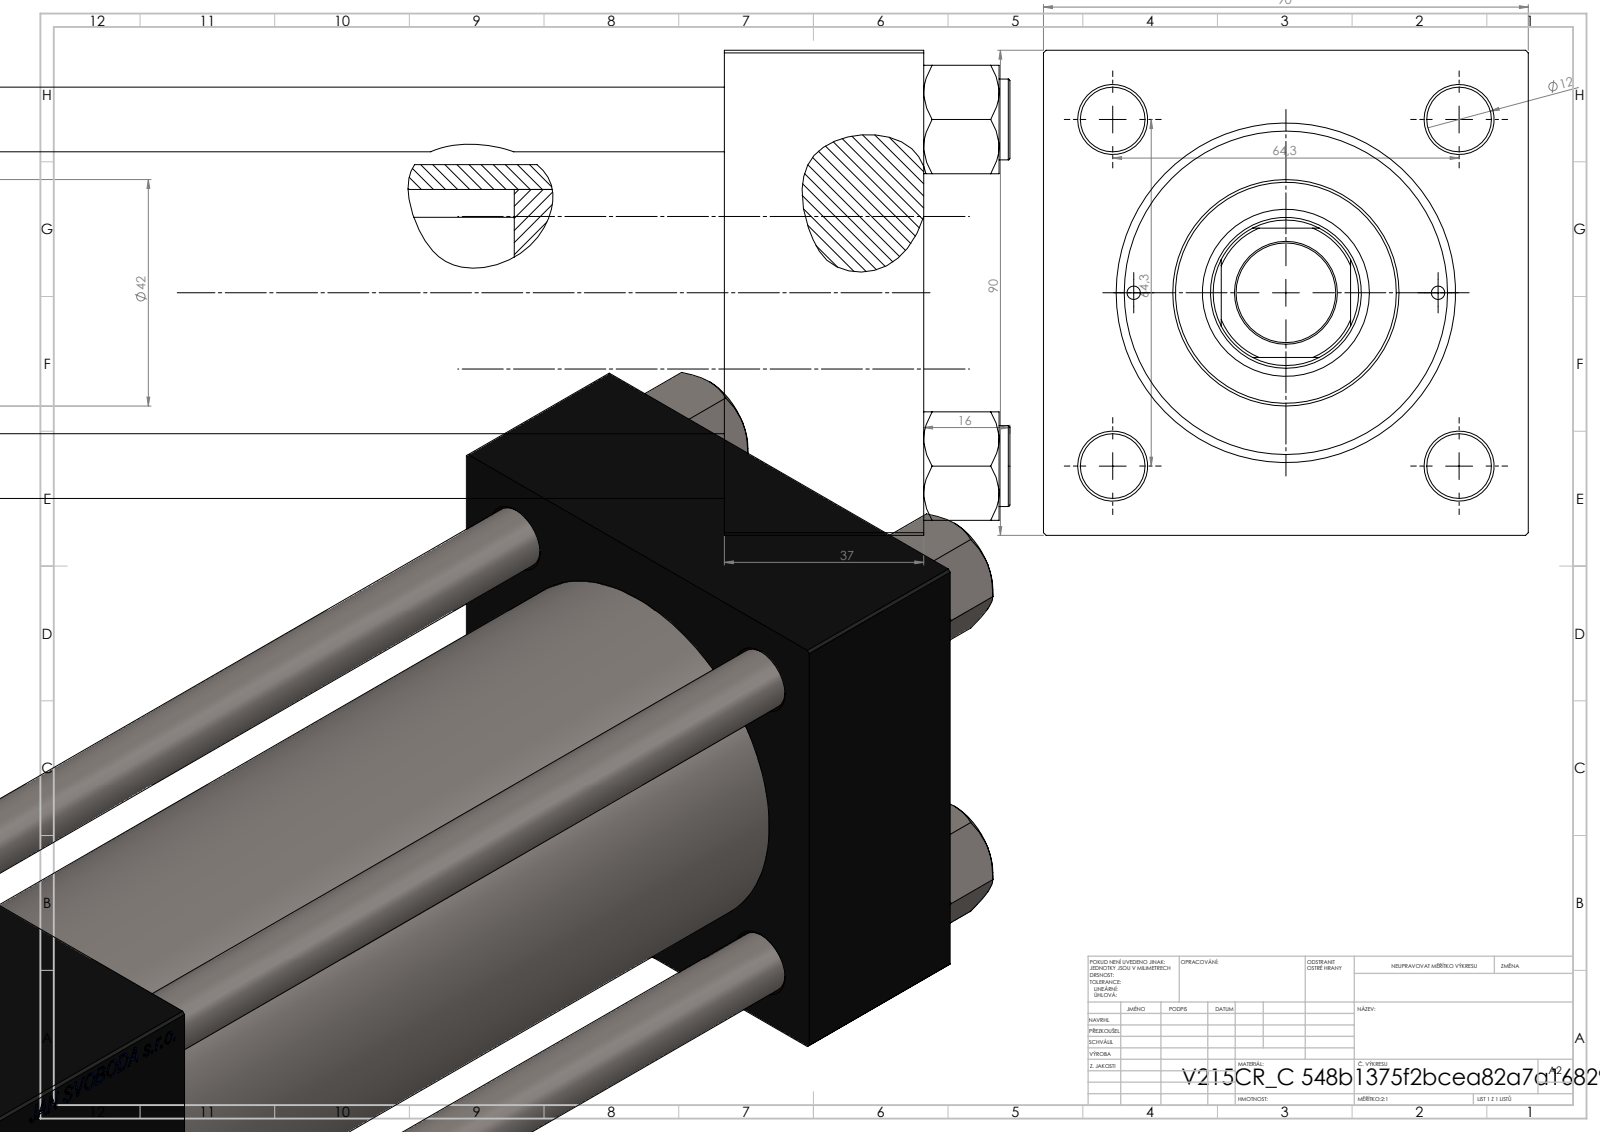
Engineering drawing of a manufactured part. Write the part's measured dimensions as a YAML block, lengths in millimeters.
part_name: "V215_VC_A; V215CR_C_Body; V215CR_C_TYCINKA; NUT_M5_C (+1 more)"
step_written_by: "SolidWorks 2019 (CONFIG_CONTROL_DESIGN)"
units: millimeters
bodies: {solids: 11, faces: 1154, planar: 528, cylindrical: 90, other: 536}
overall_size: [308, 90, 90]
volume: 1124000
surface_area: 247819
round_holes:
  - {diameter: 12, count: 4}
  - {diameter: 2.5, count: 2}
  - {diameter: 7, count: 2}
  - {diameter: 20.96, count: 2}
  - {diameter: 30, count: 2}
  - {diameter: 18.5, count: 1}
  - {diameter: 28, count: 1}
  - {diameter: 31, count: 1}
  - {diameter: 50, count: 1}
  - {diameter: 60, count: 1}
  - {diameter: 63, count: 1}
round_bosses_or_shafts:
  - {diameter: 15, count: 4}
  - {diameter: 69, count: 1}
  - {diameter: 42, count: 1}
partial_cylinders:
  - {radius: 13.5, count: 1}
face_to_face_distances: [90, 37, 260, 223, 201, 164, 59, 231.3, 194.3, 30.3]
hole_center_spacings: [32.39, 45.47, 64.3, 68.42, 28.25, 90.93, 56.5, 202.5]
